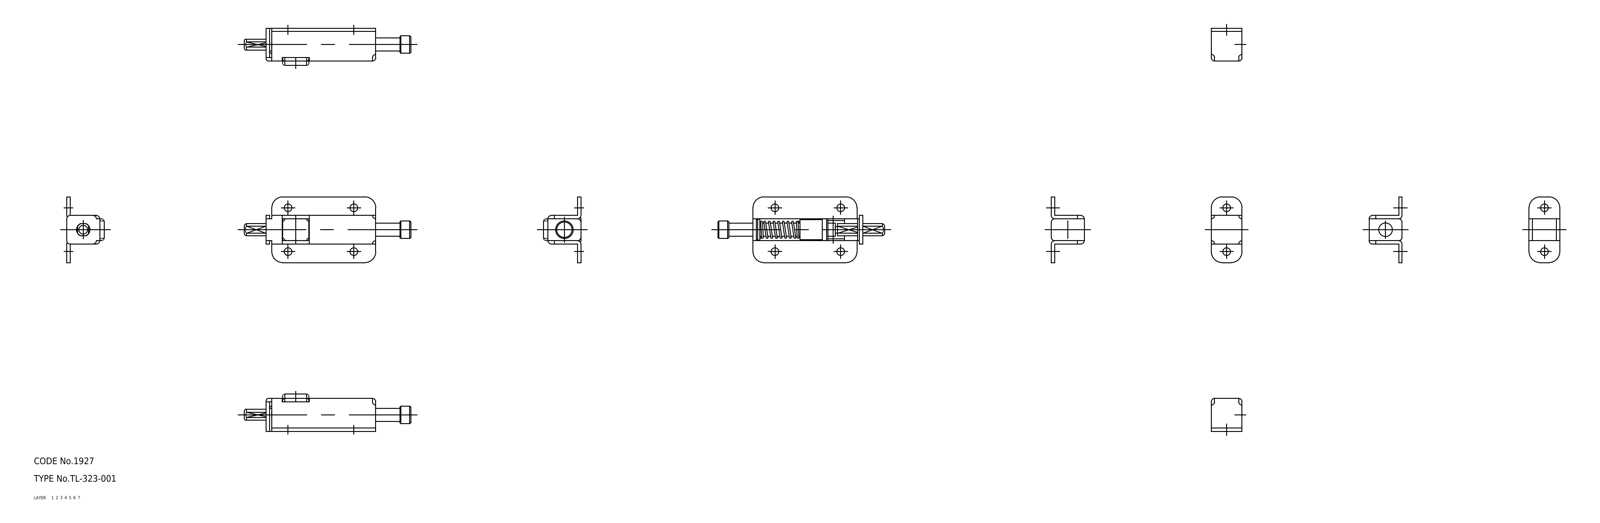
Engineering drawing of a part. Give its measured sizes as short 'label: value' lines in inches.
name: spring; spacer_2; spacer_1; retainer (+5 more)
written by: CADfix (AUTOMOTIVE_DESIGN)
unit: in
bodies: 8 solids, 321 faces (0 planar, 0 cylindrical, 321 other)
size: 3.937 × 1.181 × 0.591
volume: 0.506 in³; area: 18.35 in²
